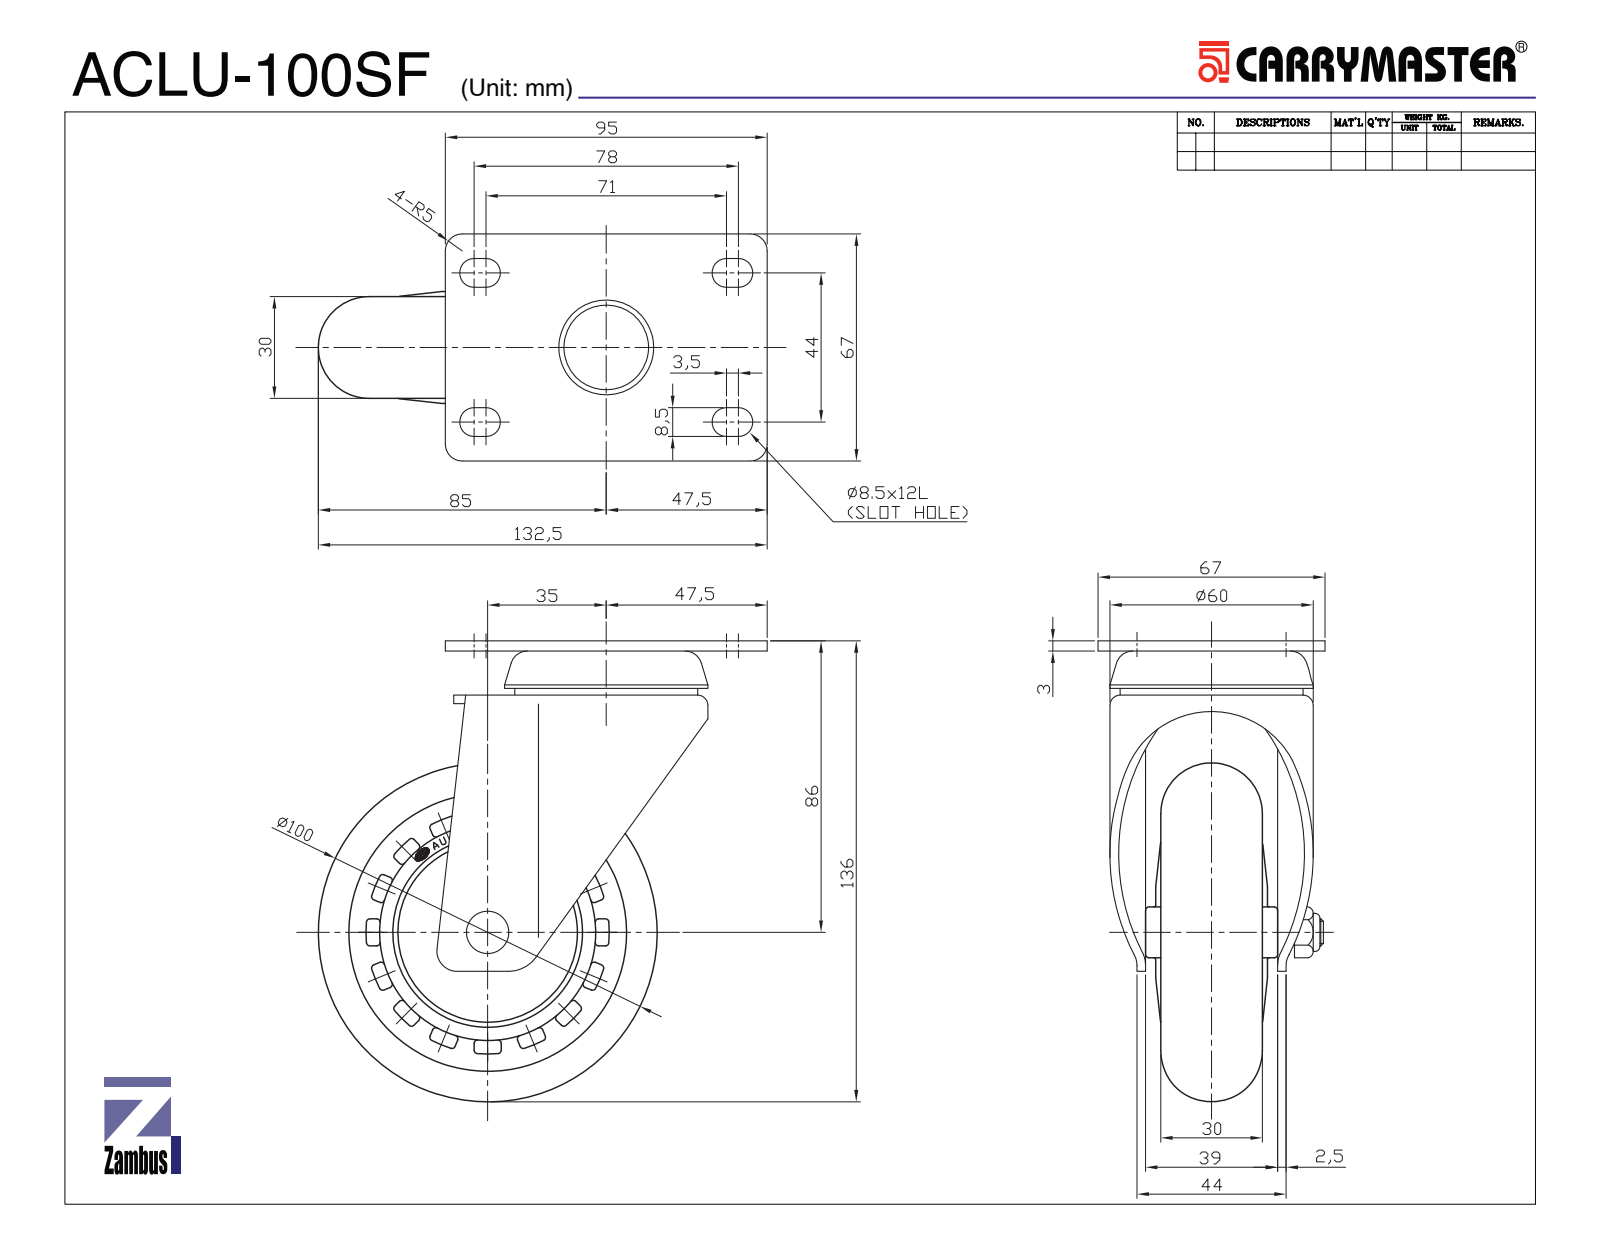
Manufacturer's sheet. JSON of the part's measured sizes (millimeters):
{"part_name": "ACLU-100SF", "step_written_by": "SolidWorks 2015 (CONFIG_CONTROL_DESIGN)", "units": "millimeters", "bodies": {"solids": 14, "faces": 1009, "planar": 510, "cylindrical": 231, "other": 268}, "overall_size": [138.78, 135.19, 69.47], "volume_mm3": 261109, "surface_area_mm2": 121824, "round_holes": [[6.8, 1], [8, 1], [9.6, 1], [12.6, 1], [19.6, 1], [22, 1], [28.62, 1], [29.82, 1], [39.2, 1], [53, 1], [55.2, 1], [64, 1]], "round_bosses_or_shafts": [[82, 1], [65.6, 1], [59.7, 1], [55, 1], [31.6, 1], [21.5, 1], [16, 1], [13, 1]], "partial_cylinders_radius": [[1, 64], [3.86, 19], [10, 18], [5, 4], [6, 4], [0.64, 2], [1.5, 2], [2.3, 2]], "face_to_face_distances": [3, 2.5, 0.5, 8.5, 5.5, 6, 8, 37.5, 43.5, 35]}
